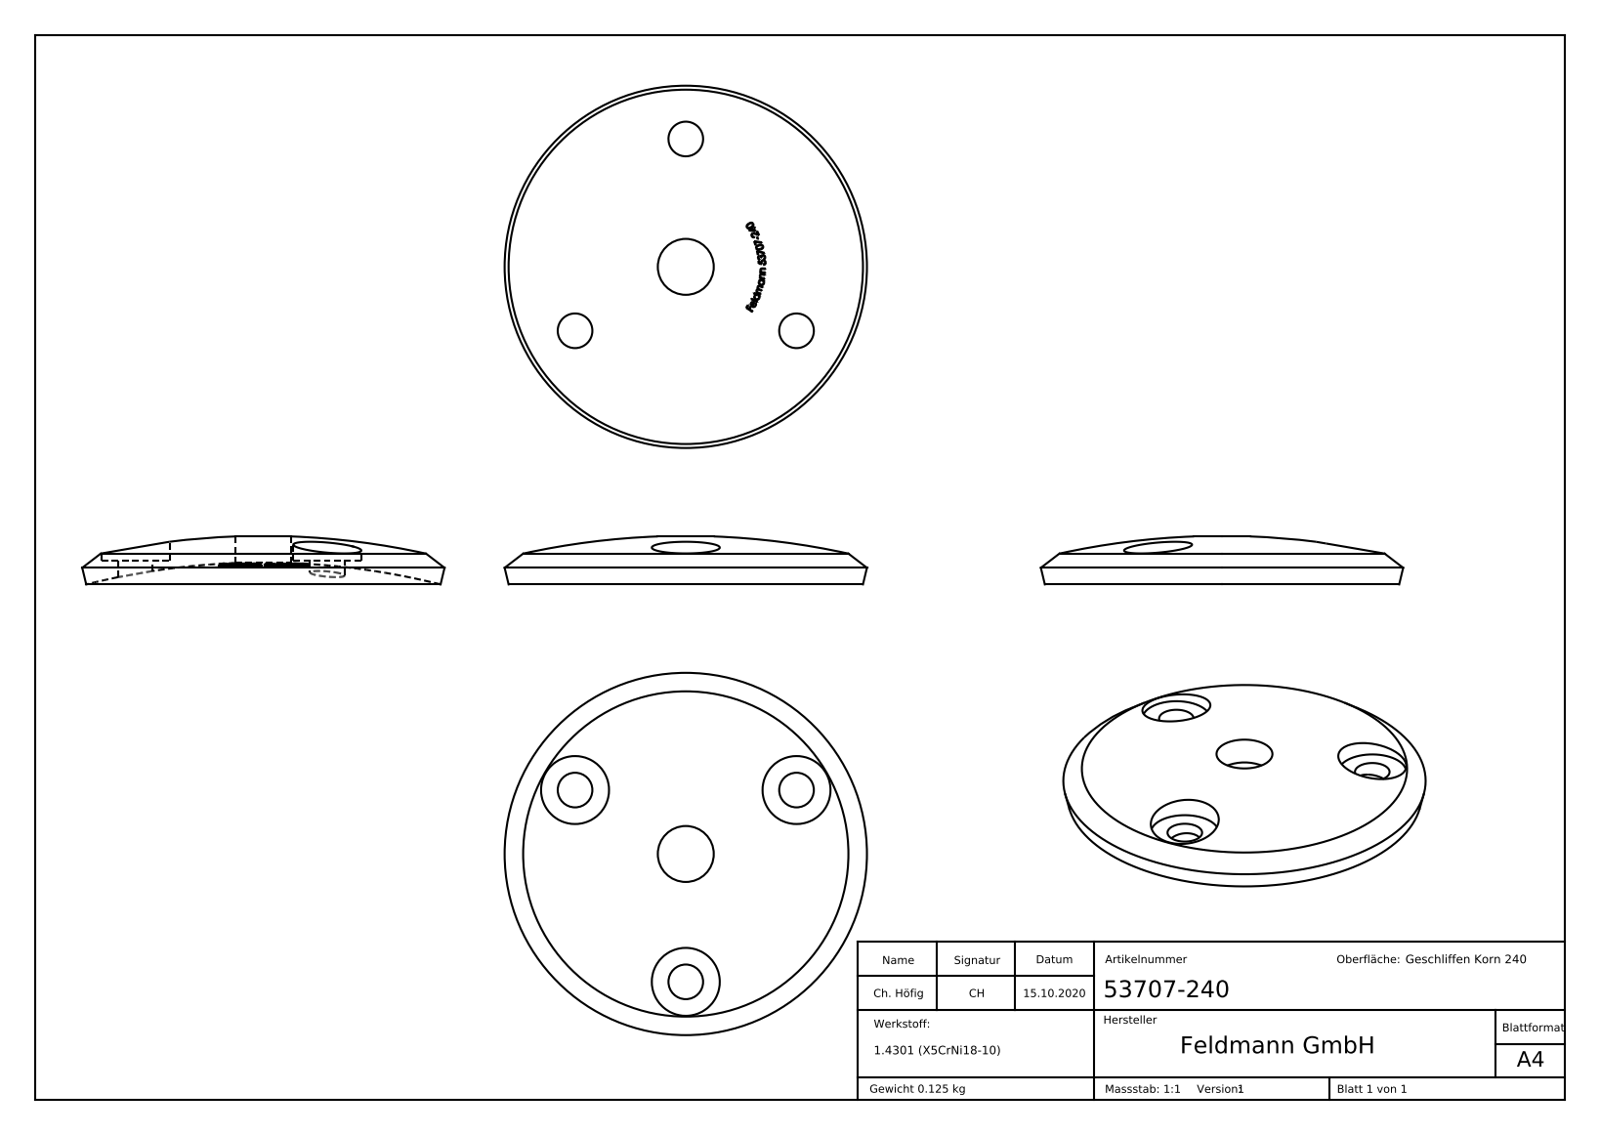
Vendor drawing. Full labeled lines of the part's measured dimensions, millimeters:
Part name (STEP PRODUCT): 53707-240
STEP written by: SolidWorks 2018 (CONFIG_CONTROL_DESIGN)
Units: millimetres
Bodies: 1 solid, 240 faces (101 planar, 14 cylindrical, 125 other)
Overall size (bounding box): 68 × 68 × 9
Volume: 15 876 mm³ · Surface area: 8 329 mm²
Round holes (diameter × count): ⌀6.5 ×3, ⌀12.75 ×3, ⌀10.5 ×1
Main face-to-face distances: 0.72, 0.54, 0.67, 0.79, 0.41, 0.85, 0.73, 0.97, 0.66, 0.6
Hole centre spacings: 24, 41.57, 41.56
